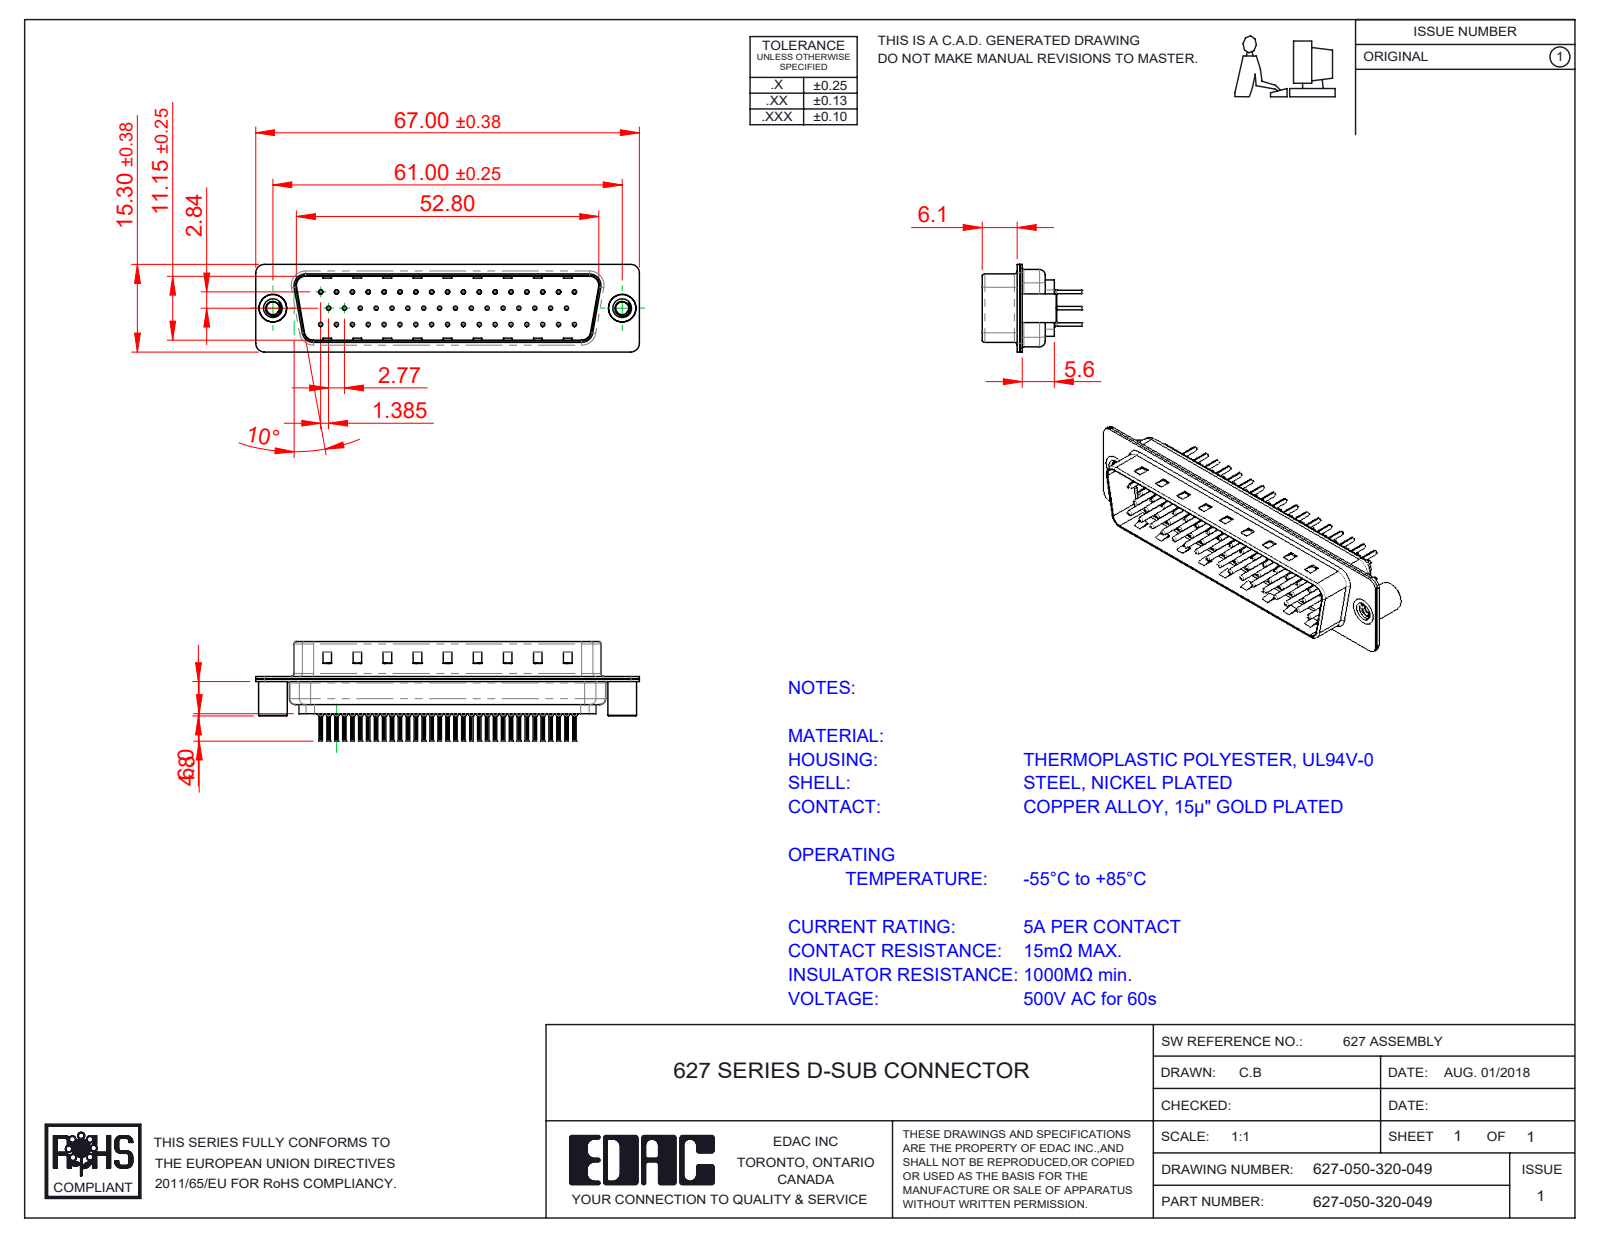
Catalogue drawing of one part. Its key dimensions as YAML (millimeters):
part_name: "627 Contact Row 2_20L; 627 Housing_50 LP; 627-050-320-049; 627 4-40 Threaded Standoff BS (+4 more)"
step_written_by: "SolidWorks 2020 (CONFIG_CONTROL_DESIGN)"
units: millimeters
bodies: {solids: 55, faces: 5334, planar: 1403, cylindrical: 2011, other: 1920}
overall_size: [67, 17.3, 15.3]
volume: 4520
surface_area: 12775
round_holes:
  - {diameter: 0.2, count: 50}
  - {diameter: 0.35, count: 50}
  - {diameter: 1.1, count: 50}
  - {diameter: 1.6, count: 50}
  - {diameter: 2.26, count: 2}
  - {diameter: 4, count: 2}
  - {diameter: 4.8, count: 2}
round_bosses_or_shafts:
  - {diameter: 2, count: 50}
  - {diameter: 1.5, count: 50}
  - {diameter: 0.75, count: 50}
  - {diameter: 0.6, count: 50}
  - {diameter: 5, count: 2}
  - {diameter: 4.9, count: 2}
partial_cylinders:
  - {radius: 0.1, count: 100}
  - {radius: 1.5, count: 16}
  - {radius: 2, count: 12}
  - {radius: 0.5, count: 8}
  - {radius: 1.6, count: 8}
  - {radius: 0.25, count: 4}
  - {radius: 0.6, count: 4}
  - {radius: 0.65, count: 4}
face_to_face_distances: [0.4, 0.45, 11.55, 0.9, 6.05, 6.5, 0.78, 12.33, 1.95, 0.77]
hole_center_spacings: [3.16, 2.77, 5.54, 8.31, 11.08, 13.85, 16.62, 5.03]
